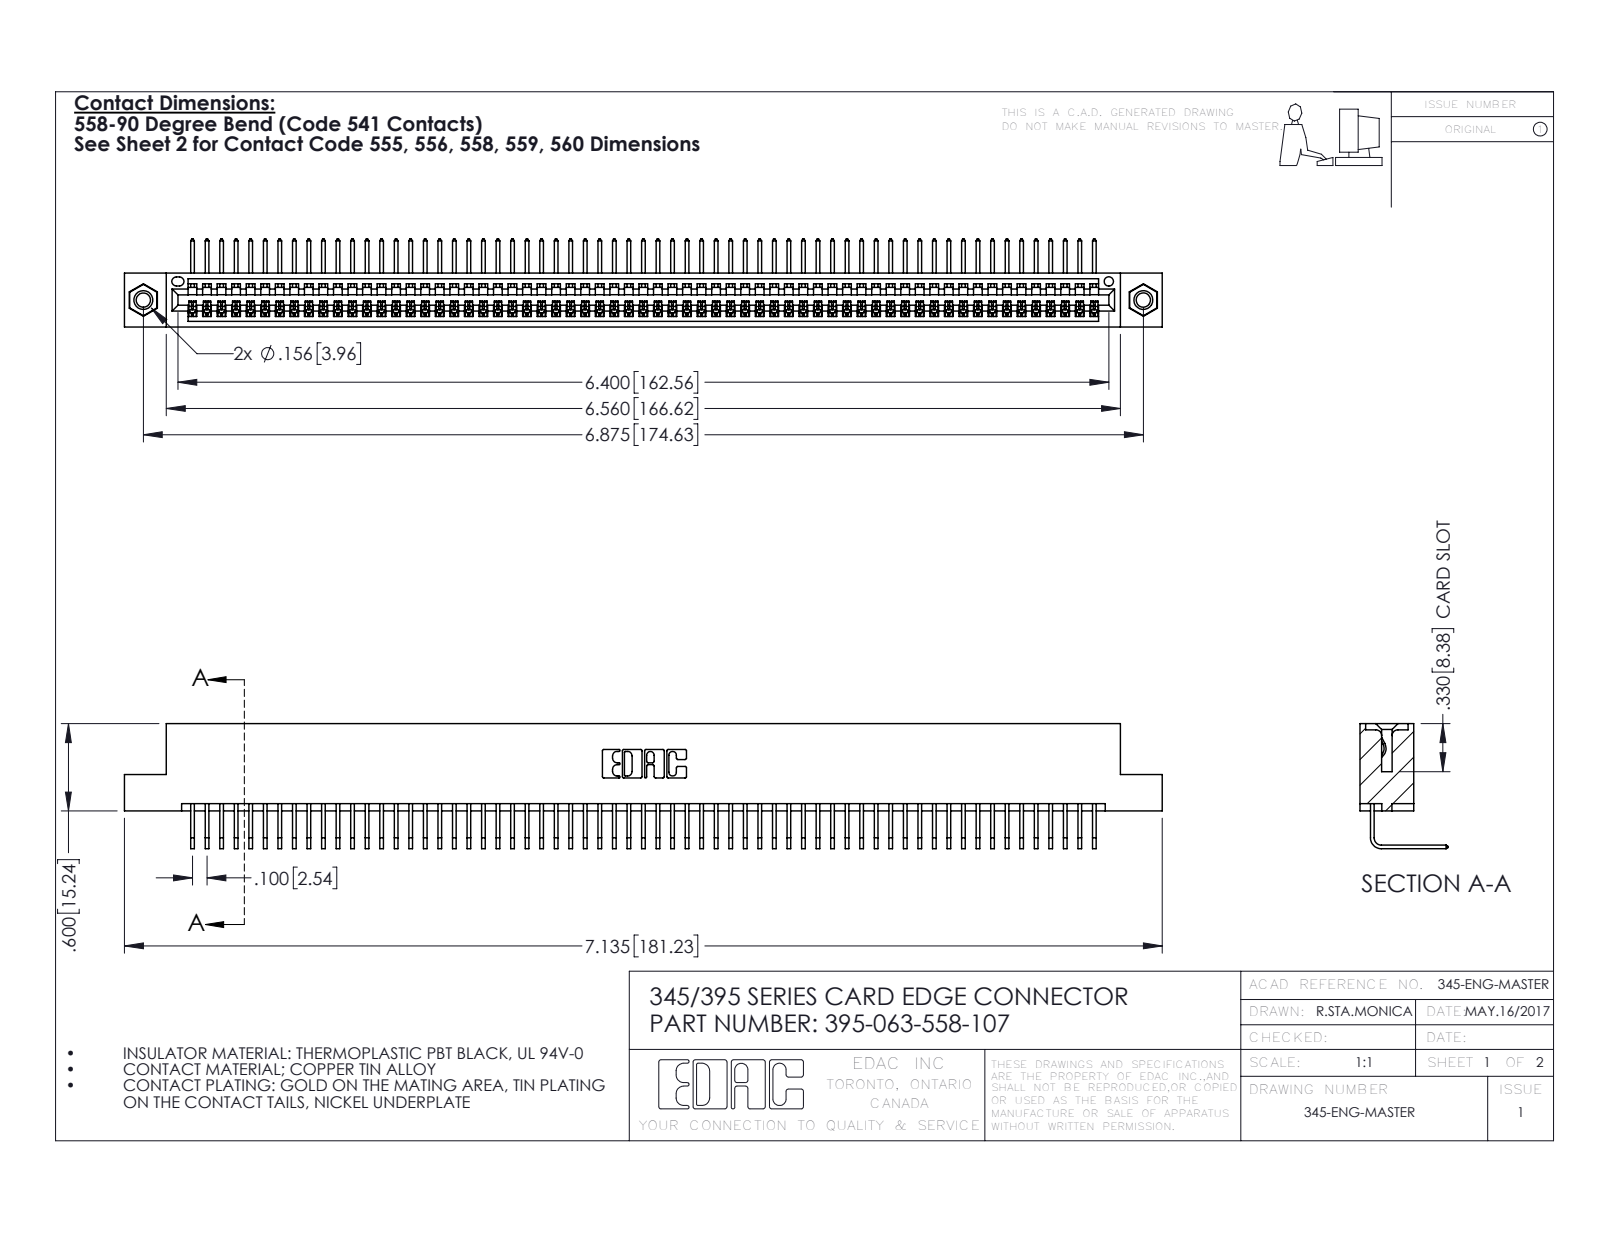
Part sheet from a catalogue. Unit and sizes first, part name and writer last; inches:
Units: inches
Overall size (bounding box): 7.135 × 0.859 × 0.605
Round holes (diameter × count): ⌀0.098 ×2, ⌀0.125 ×2, ⌀0.156 ×2, ⌀0.064 ×1
Round bosses / shafts (diameter × count): ⌀0.155 ×2
Partial cylindrical surfaces — rounded edges, fillets, slot ends (radius × count): R0.006 ×126, R0.01 ×22, R0.007 ×6, R0.031 ×6, R0.026 ×3, R0.031 ×2, R0.04 ×2, R0.014 ×1
Main face-to-face distances: 0.072, 0.298, 0.37, 0.2, 0.098, 0.272, 0.025, 0.225, 0.149, 0.072
Hole centre spacings: 0.27, 6.639, 6.875
Volume: 1.073 in³ · Surface area: 38.62 in²
Bodies: 66 solids, 3966 faces (2758 planar, 1192 cylindrical, 16 other)
Part name (STEP PRODUCT): 345-292-001_558 Tail - 2; 395-063-558-107; 345 Part_Flush Mounting Lugs - 0.156 Dia-TI; 345-250-001_345-250-005-103
STEP written by: SolidWorks 2016 (CONFIG_CONTROL_DESIGN)
